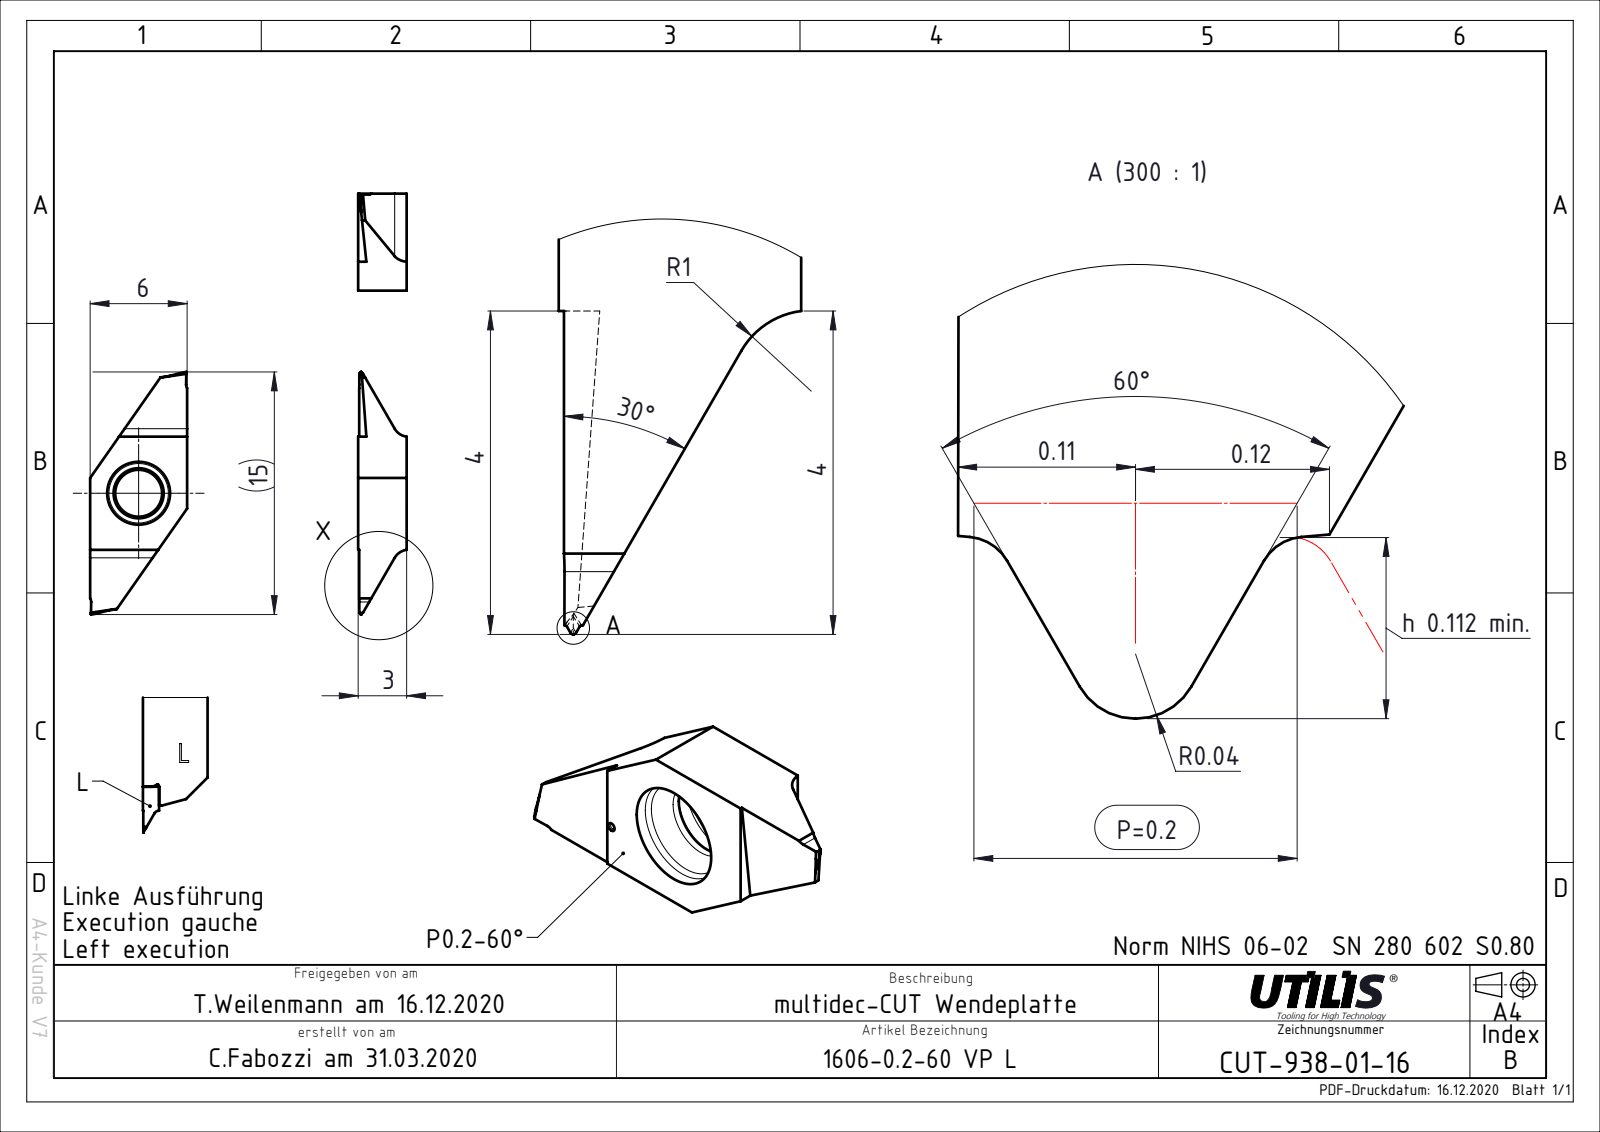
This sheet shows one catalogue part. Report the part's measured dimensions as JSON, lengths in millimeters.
{"part_name": "CUT-938-01; ASME Y14.5", "step_written_by": "FormatWorks Professional (AP242_MANAGED_MODEL_BASED_3D_ENGINEERING_MIM_LF)", "units": "millimeters", "bodies": {"solids": 1, "faces": 36, "planar": 22, "cylindrical": 14, "other": 0}, "overall_size": [15, 6, 3], "volume_mm3": 126, "surface_area_mm2": 210, "round_holes": [[2.9, 1]], "partial_cylinders_radius": [[1, 2]], "face_to_face_distances": [6, 3, 9, 7, 12, 7.22, 14.4, 14.41]}
